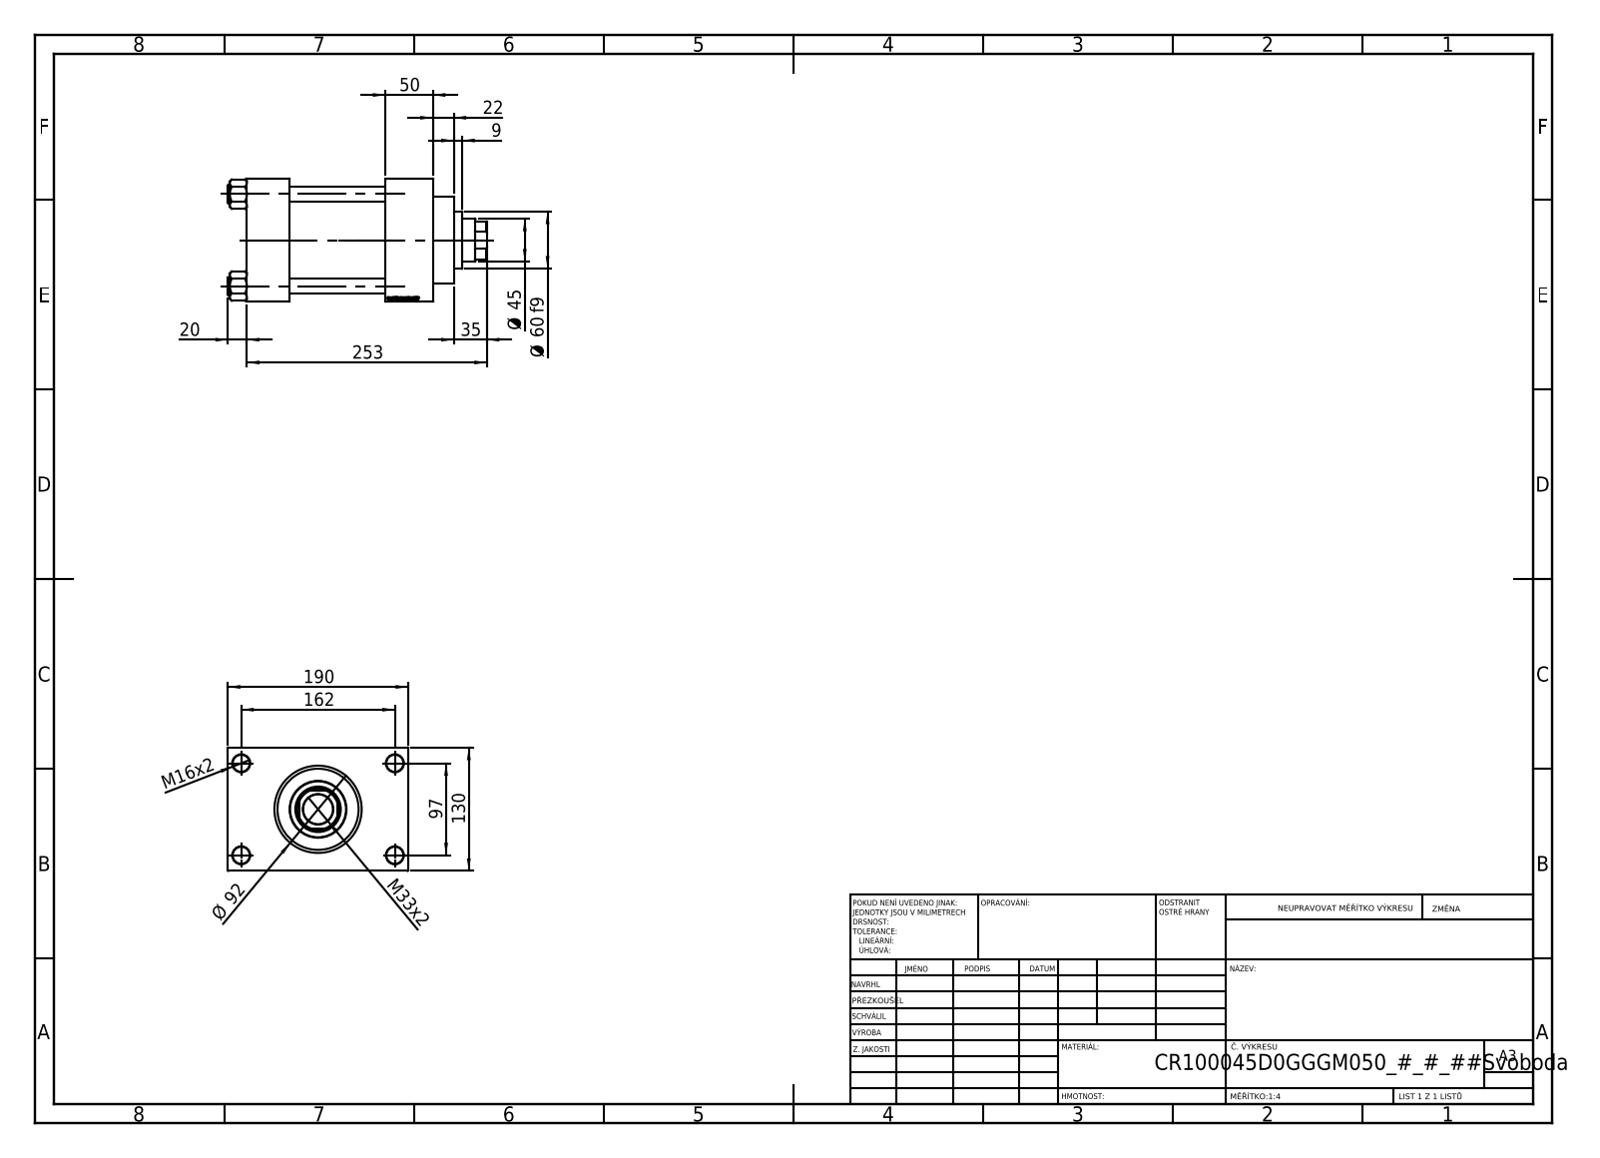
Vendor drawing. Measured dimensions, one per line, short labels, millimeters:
name: V215CR_D_Body; V215CR_VCP_D; V215CR_D_TYCINKA; NUT_M5_D (+1 more)
written by: SolidWorks 2019 (CONFIG_CONTROL_DESIGN)
unit: mm
bodies: 11 solids, 1152 faces (545 planar, 89 cylindrical, 518 other)
size: 273 × 190 × 130
volume: 2 708 000 mm³; area: 382 082 mm²
holes: 4× ⌀16, 4× ⌀18, 2× ⌀7, 2× ⌀26.44, 2× ⌀35, 1× ⌀31.5, 1× ⌀45, 1× ⌀48, 1× ⌀76, 1× ⌀85.5, 1× ⌀100
bosses: 4× ⌀19, 1× ⌀106, 1× ⌀92, 1× ⌀60
rounds: 1× R22
face distances: 50, 130, 45, 146, 101, 196, 151, 30, 160, 190
hole spacings: 32.55, 68.52, 94.41, 96.9, 102.27, 129.45, 161.73, 97
